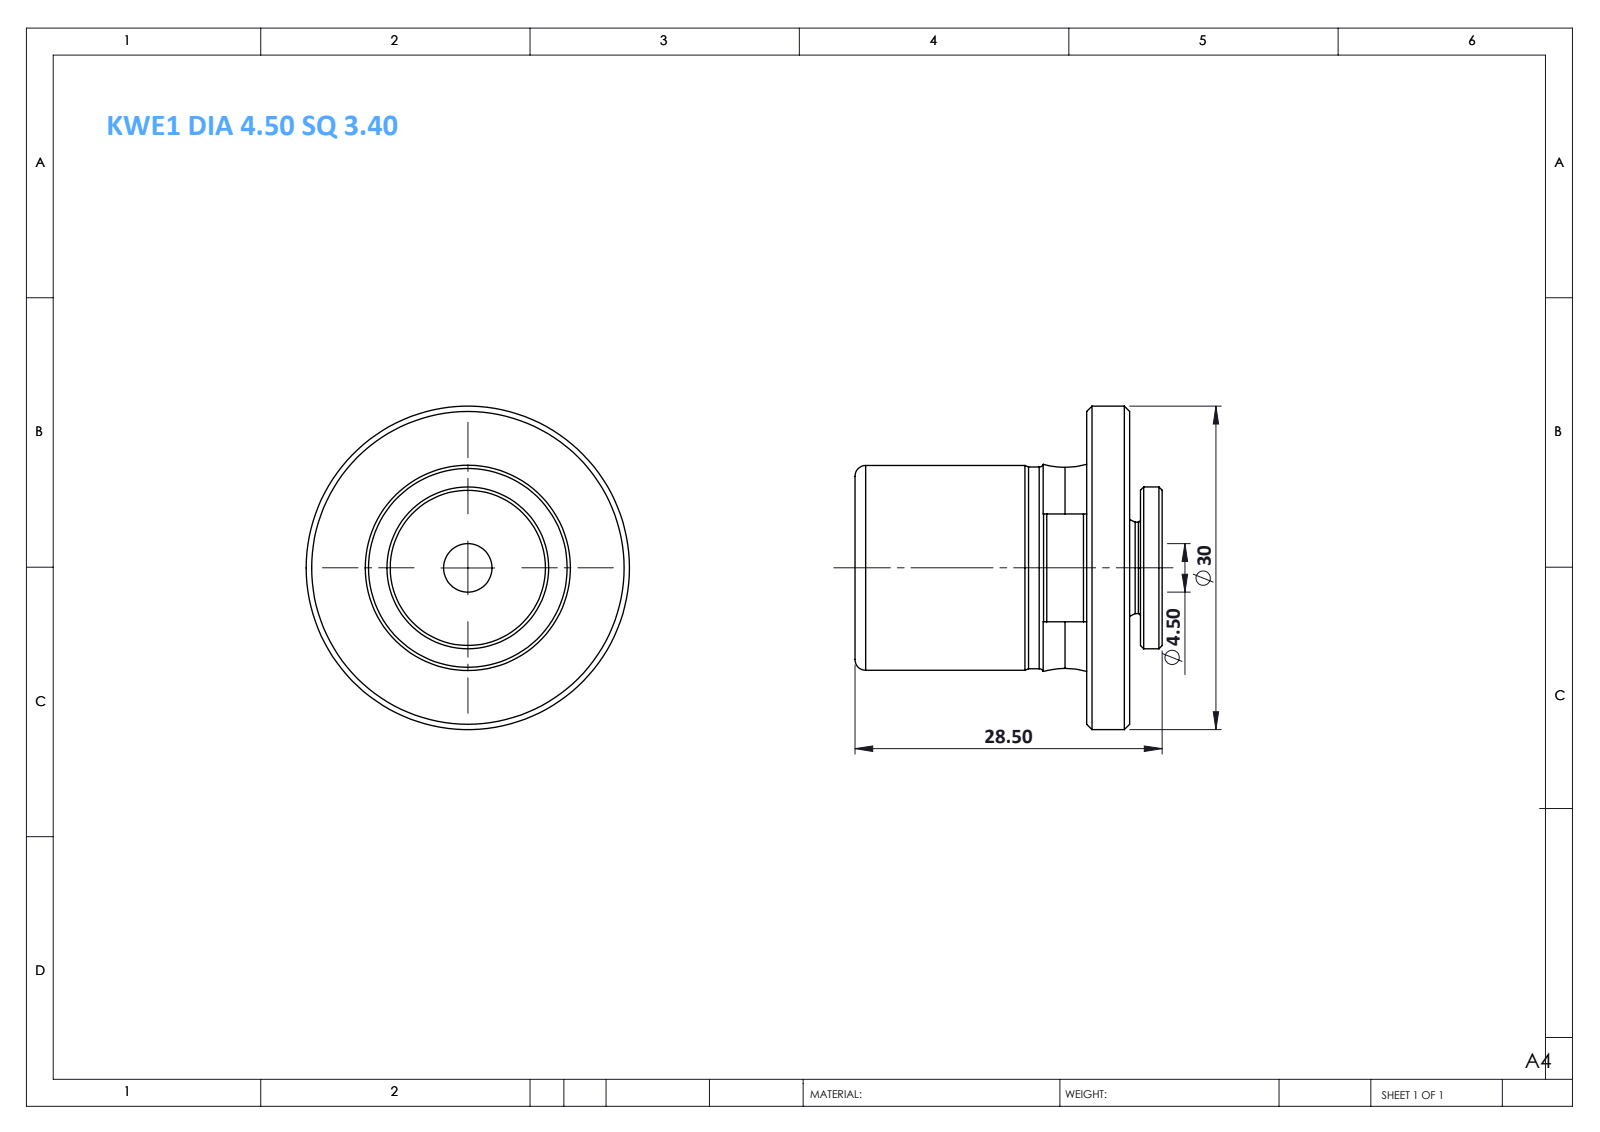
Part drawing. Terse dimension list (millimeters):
name: KWE1 DIA 4.50 SQ 3.4
written by: SolidWorks 2014 (CONFIG_CONTROL_DESIGN)
unit: mm
bodies: 1 solid, 59 faces (13 planar, 16 cylindrical, 30 other)
size: 30 × 30 × 28.5
volume: 9 269 mm³; area: 3 624 mm²
holes: 1× ⌀4.5, 1× ⌀19.04
bosses: 1× ⌀30, 1× ⌀19, 1× ⌀18.7, 1× ⌀15, 1× ⌀8.5
rounds: 1× R12.4
face distances: 4, 21.5, 25.5, 28.5, 7, 3, 26.5, 5, 1, 2
